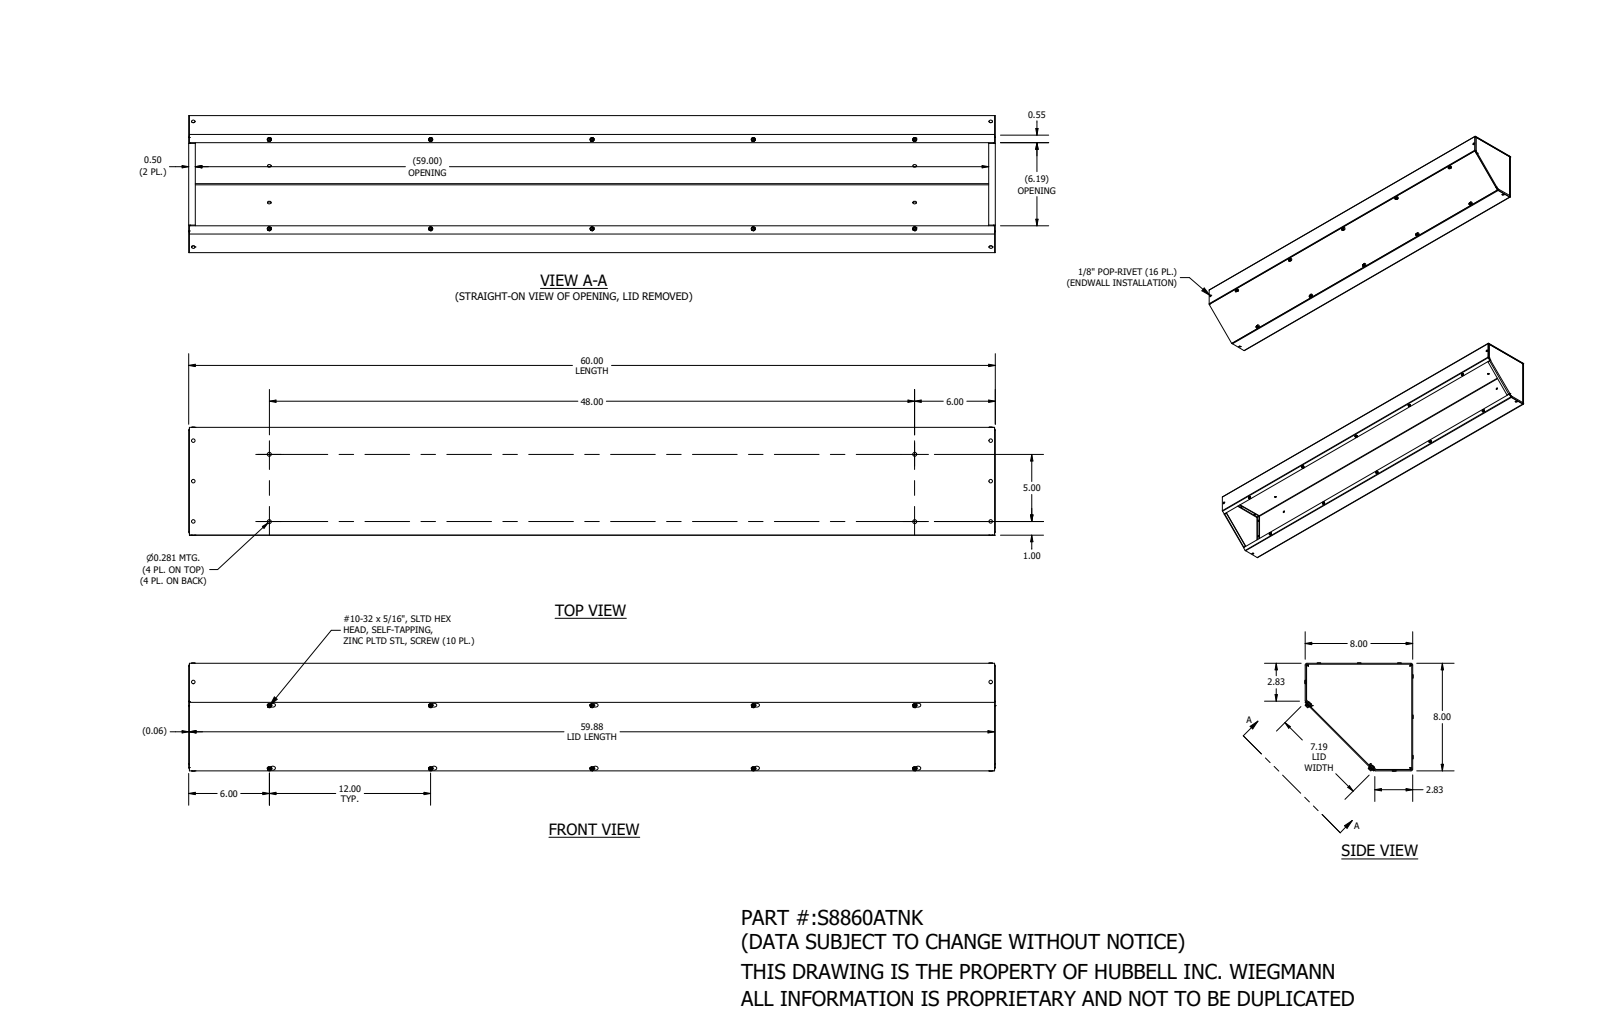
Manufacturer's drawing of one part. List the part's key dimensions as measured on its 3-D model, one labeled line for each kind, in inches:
Part name (STEP PRODUCT): S8860ATNK
STEP written by: SolidWorks 2021 (AUTOMOTIVE_DESIGN)
Units: inches
Bodies: 30 solids, 1946 faces (430 planar, 504 cylindrical, 1012 other)
Overall size (bounding box): 60 × 8.08 × 8.08
Volume: 139.7 in³ · Surface area: 3 809 in²
Round holes (diameter × count): ⌀0.129 ×16, ⌀0.171 ×10, ⌀0.406 ×10, ⌀0.281 ×8
Round bosses / shafts (diameter × count): ⌀0.262 ×16, ⌀0.313 ×10, ⌀0.181 ×10, ⌀0.125 ×10, ⌀0.125 ×6
Partial cylindrical surfaces — rounded edges, fillets, slot ends (radius × count): R0.064 ×32, R0.136 ×15, R0.109 ×10, R0.062 ×8, R0.063 ×7
Main face-to-face distances: 0.074, 7.926, 7.852, 8, 0.068, 59.926, 0.142, 59.852, 60, 0.148
Hole centre spacings: 12, 24, 0.25, 3, 11.75, 12.25, 13.707, 13.711
